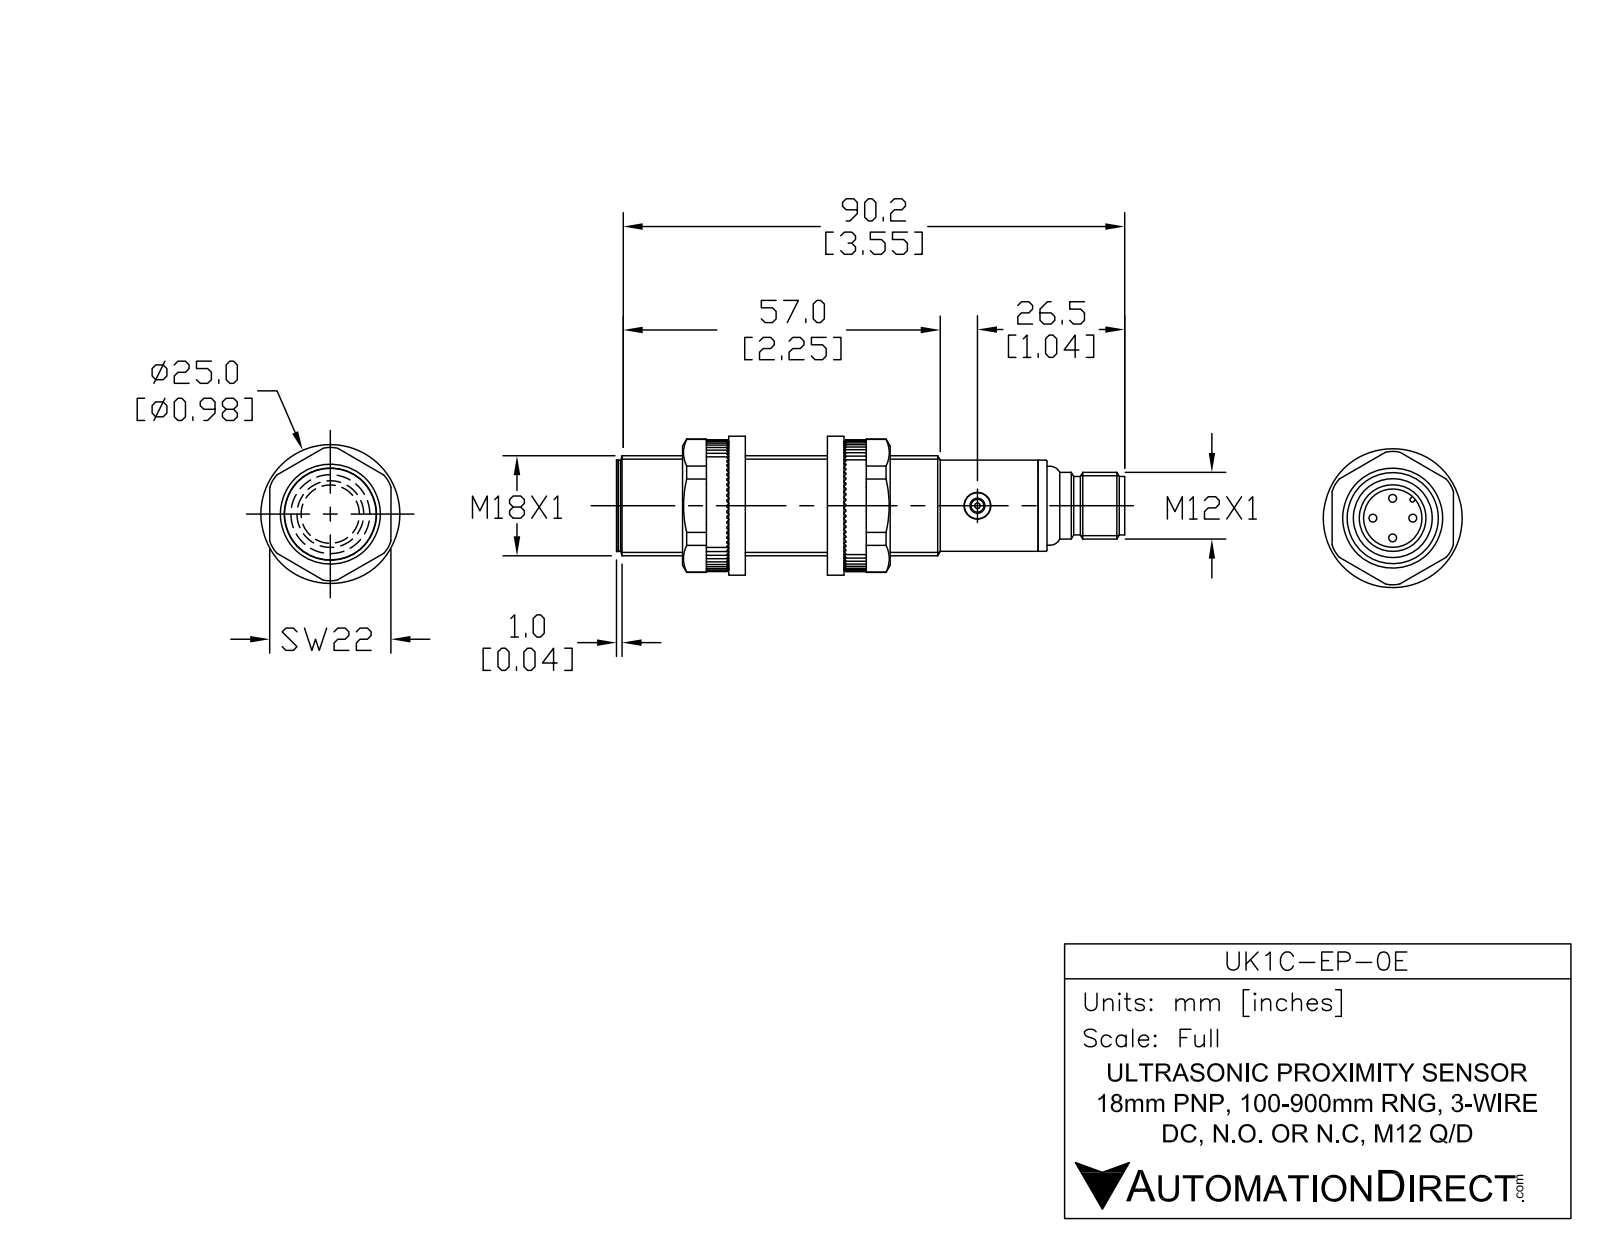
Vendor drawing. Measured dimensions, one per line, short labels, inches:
name: UK1C-EP-0E
written by: SolidWorks 2017 (AUTOMOTIVE_DESIGN)
unit: in
bodies: 6 solids, 106 faces (21 planar, 48 cylindrical, 37 other)
size: 3.606 × 0.709 × 0.709
volume: 1.202 in³; area: 10.68 in²
holes: 1× ⌀0.106, 1× ⌀0.185, 1× ⌀0.276, 1× ⌀0.327, 1× ⌀0.374
bosses: 4× ⌀0.039, 1× ⌀0.709, 1× ⌀0.654, 1× ⌀0.646, 1× ⌀0.622, 1× ⌀0.559, 1× ⌀0.472, 1× ⌀0.413
rounds: 1× R0.024
face distances: 2.957, 0.039, 2.996, 0.037, 2.994, 0.043, 0.157, 3.055, 3.053, 3.016
